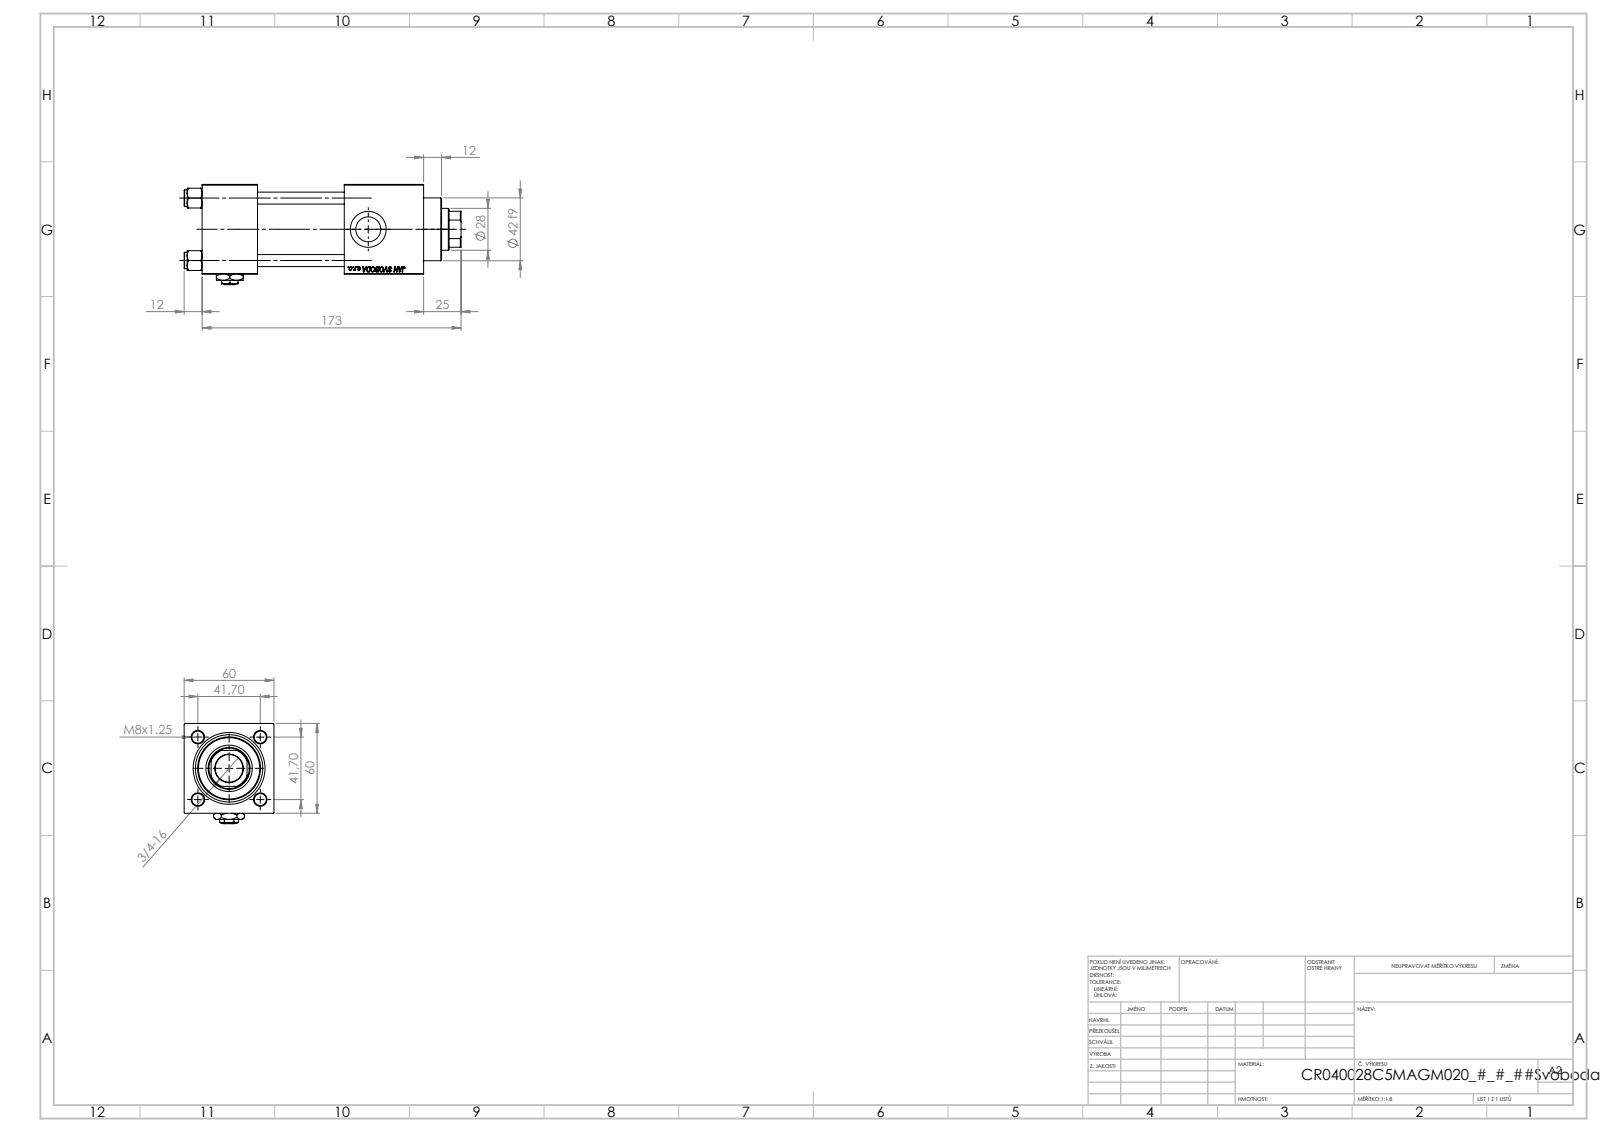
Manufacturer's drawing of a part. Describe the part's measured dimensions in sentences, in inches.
The part is named "Zatka_pro_OIL_PORT; V215CR_VCP_C; V215_VC_A; V215CR_C_Body (+2 more)". Its 3-D file was written by "SolidWorks 2019 (CONFIG_CONTROL_DESIGN)". It is 12 solids with 1202 faces: 550 planar, 94 cylindrical and 558 other. Overall it measures 7.283 by 2.638 by 2.362 inches. Its volume is 25.77 cubic inches and its surface area 175.4 square inches. Round holes: 4 of diameter 0.315, 2 of diameter 0.276, 2 of diameter 0.656, 2 of diameter 0.945, 1 of diameter 0.728, 1 of diameter 1.102, 1 of diameter 1.22, 1 of diameter 1.575, 1 of diameter 1.772. Round bosses or shafts: 4 of diameter 0.433, 1 of diameter 1.811, 1 of diameter 1.654. Partial cylindrical surfaces (rounded edges, fillets, slot ends): 1 of radius 0.531. The main face-to-face distances are 2.362, 1.457, 2.283, 3.74, 2.087, 4.697, 3.24, 0.957, 5.827, 4.37. The hole center spacings are 1.161, 1.642, 2.322.
